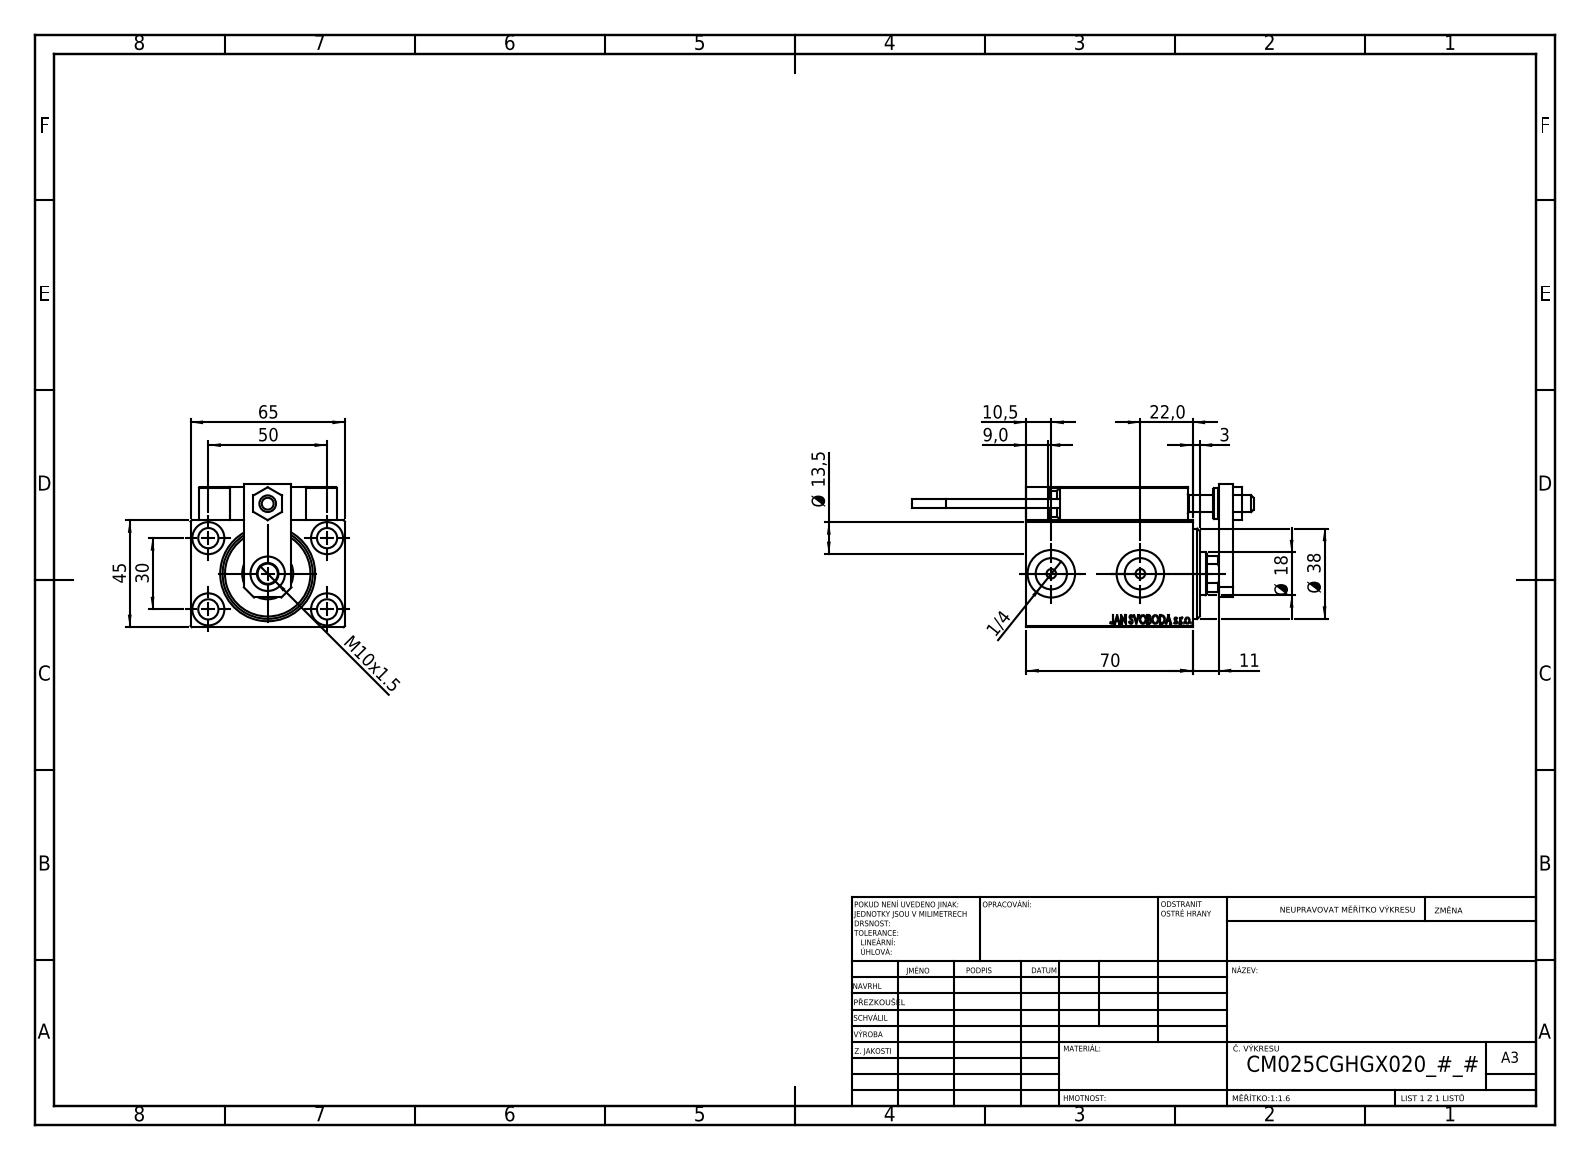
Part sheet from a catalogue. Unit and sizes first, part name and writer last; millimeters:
Units: millimetres
Overall size (bounding box): 143.7 × 65 × 60.5
Round holes (diameter × count): ⌀4 ×6, ⌀8 ×5, ⌀8.5 ×5, ⌀3.2 ×4, ⌀13.5 ×4, ⌀5 ×2, ⌀13.16 ×2, ⌀20 ×2, ⌀7 ×1, ⌀14.5 ×1, ⌀18 ×1, ⌀21.5 ×1
Round bosses / shafts (diameter × count): ⌀5 ×2, ⌀3.8 ×2, ⌀13 ×1, ⌀11 ×1
Partial cylindrical surfaces — rounded edges, fillets, slot ends (radius × count): R0.3 ×30, R3 ×2, R8.5 ×1
Main face-to-face distances: 45, 59, 14, 65, 6, 3, 19, 5, 13, 7
Hole centre spacings: 29.15, 11.37, 20, 22.09, 28.9, 29.59, 29.69, 30
Volume: 223 110 mm³ · Surface area: 69 190 mm²
Bodies: 23 solids, 1282 faces (560 planar, 188 cylindrical, 534 other)
Part name (STEP PRODUCT): V450CM_VC_B; MAGNET; ALLEN BOLT D8; KONCOVKA (+8 more)
STEP written by: SolidWorks 2019 (CONFIG_CONTROL_DESIGN)
